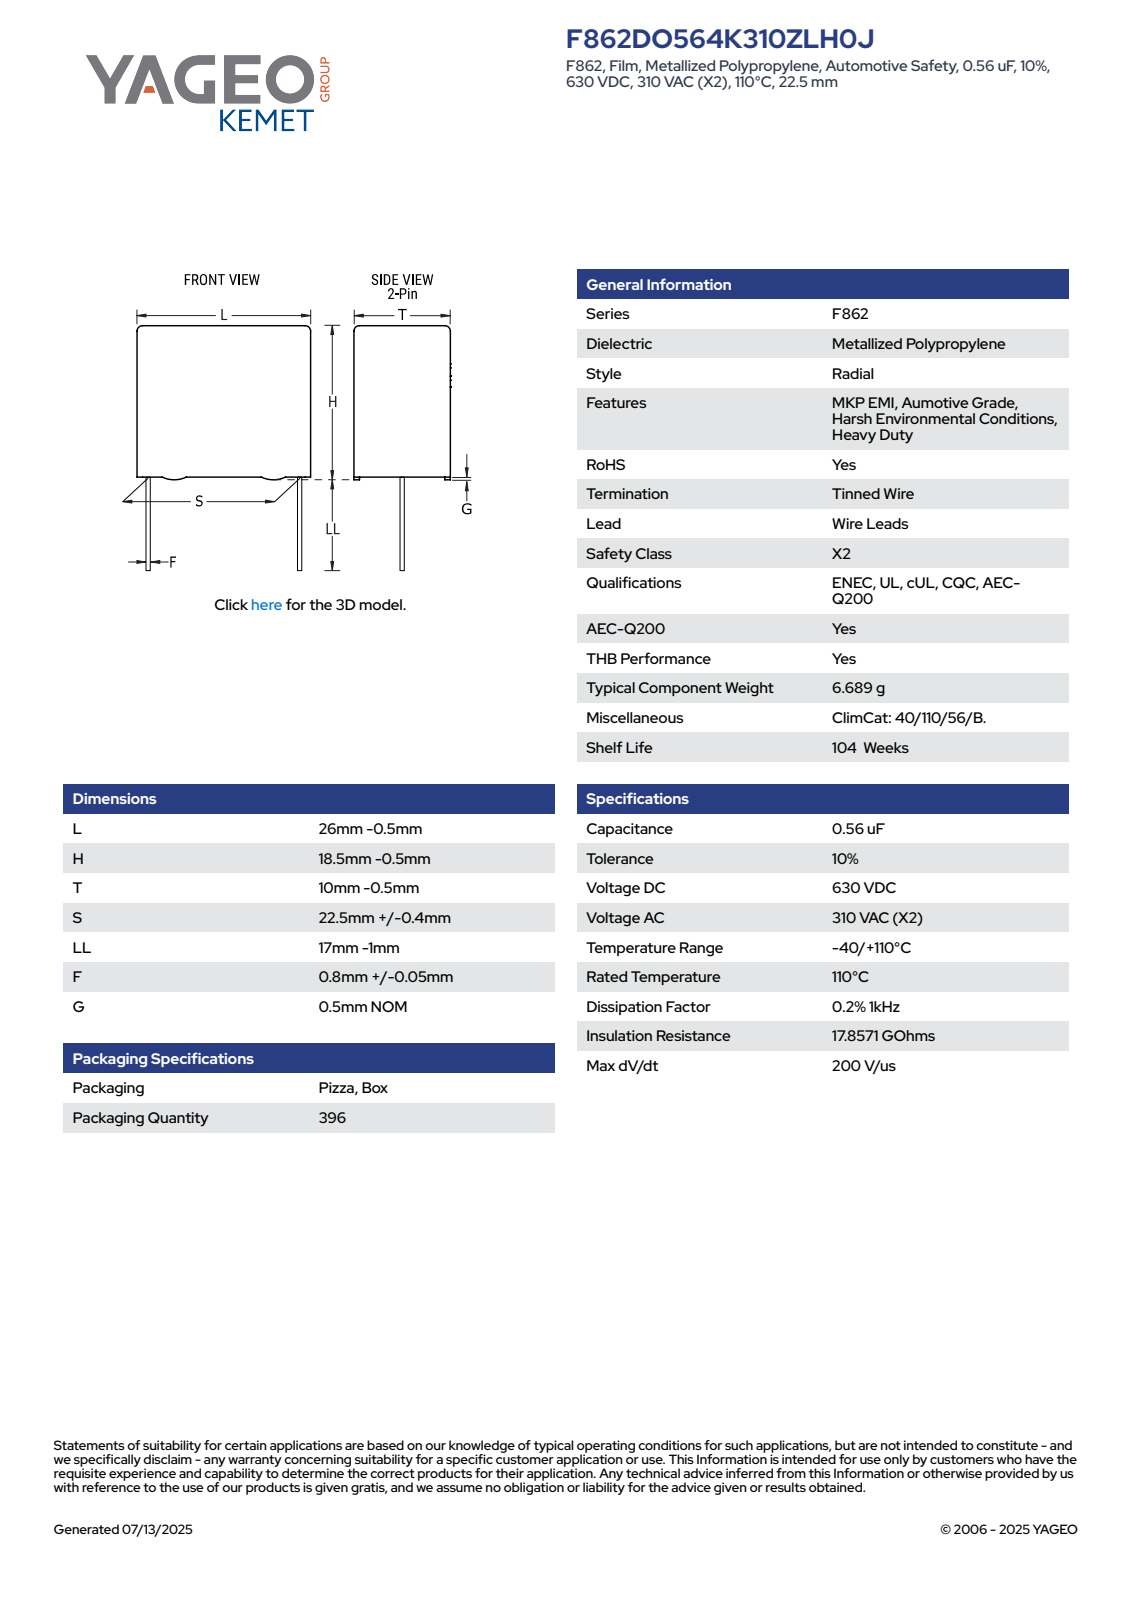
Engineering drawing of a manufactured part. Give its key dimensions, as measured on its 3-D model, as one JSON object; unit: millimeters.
{"part_name": "CFR_RBG_26X18.5X10_L25.5H18T9.5S22.5LL16F0.85G0.5", "step_written_by": "SolidWorks 2014 (AUTOMOTIVE_DESIGN)", "units": "millimeters", "bodies": {"solids": 4, "faces": 89, "planar": 81, "cylindrical": 8, "other": 0}, "overall_size": [34, 25.5, 9.51], "volume_mm3": 4259, "surface_area_mm2": 1870, "round_bosses_or_shafts": [[0.85, 2]], "partial_cylinders_radius": [[0.5, 4]], "face_to_face_distances": [9.5, 17.5, 25.5, 0.5, 18, 0.54, 8.96, 8.42, 16, 16.5]}
